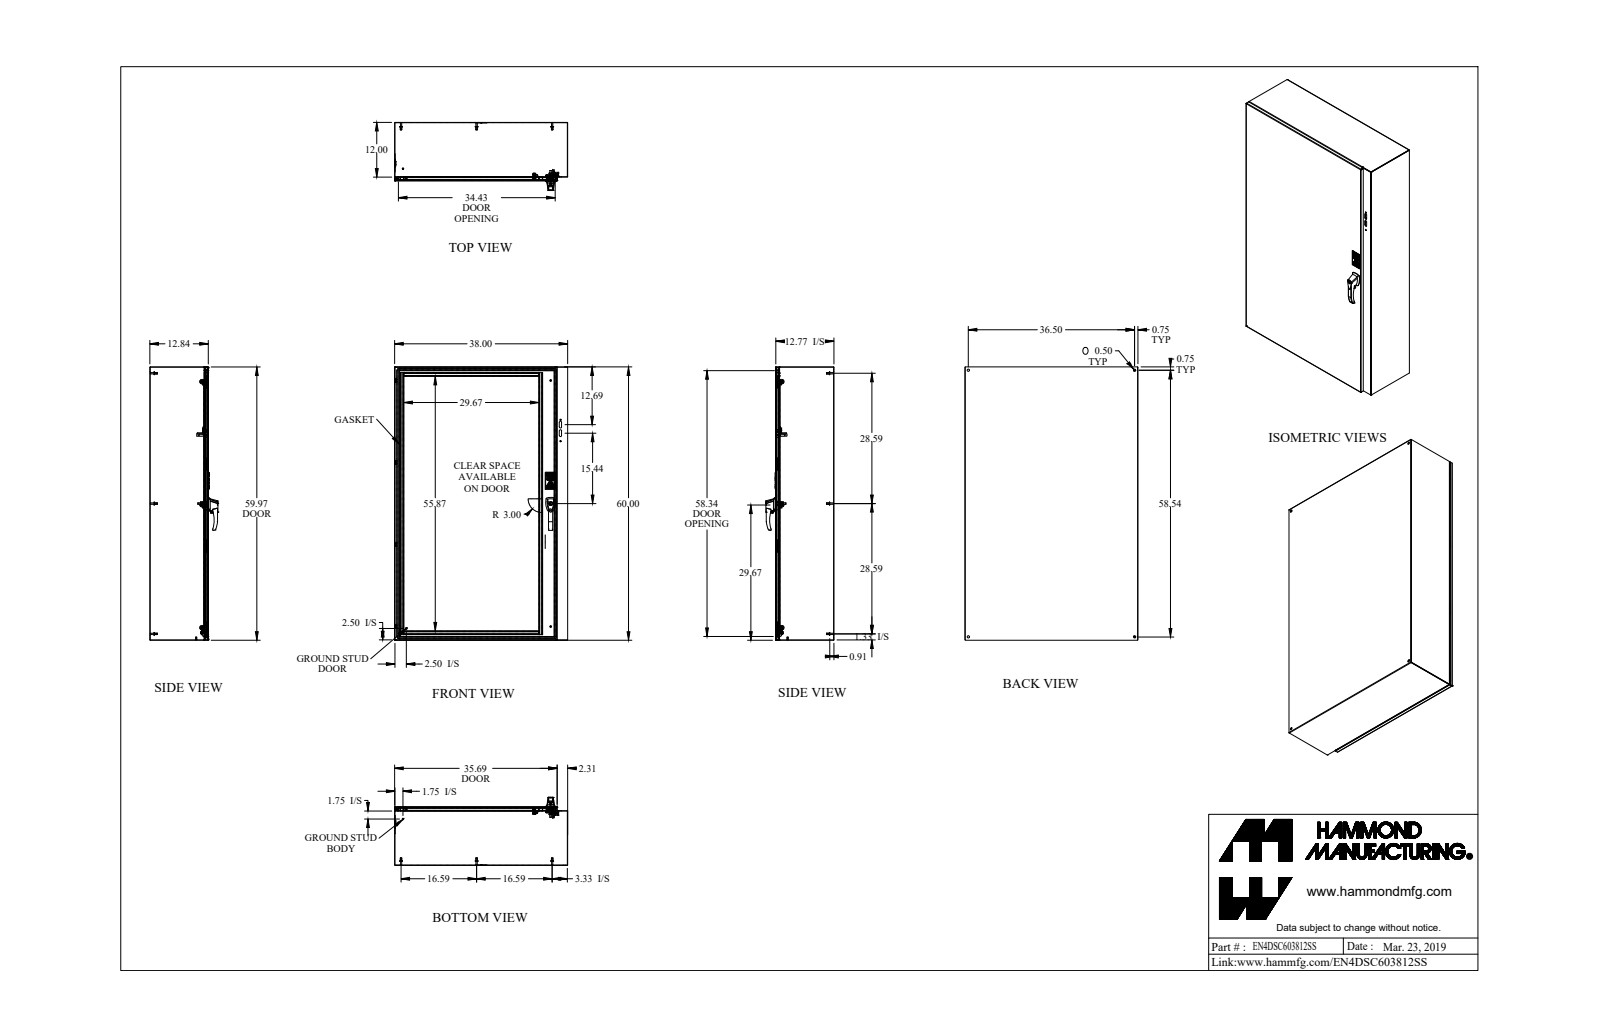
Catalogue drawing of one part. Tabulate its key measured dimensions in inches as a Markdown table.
| quantity | value |
| --- | --- |
| part name | EN4DSC603812SS |
| STEP written by | SolidWorks 2019 (AUTOMOTIVE_DESIGN) |
| units | inches |
| bodies | 75 solids, 1578 faces (889 planar, 476 cylindrical, 213 other) |
| overall size | 60 × 38 × 14.952 |
| volume | 582.6 in³ |
| surface area | 16 197 in² |
| round holes (diameter × count) | 0.176 × 6, 0.5 × 4, 0.196 × 3, 0.25 × 3, 0.265 × 3, 0.413 × 3, 0.156 × 2, 0.173 × 2, 0.215 × 2, 0.256 × 2, 0.281 × 2, 0.313 × 2 |
| round bosses / shafts (diameter × count) | 0.25 × 9, 0.625 × 8, 0.313 × 8, 0.27 × 8, 0.156 × 6, 0.375 × 5, 1 × 3, 0.63 × 2 |
| partial cylindrical surfaces (radius × count) | 0.043 × 24, 0.036 × 18, 0.108 × 18, 0.062 × 17, 0.25 × 15, 0.03 × 14, 0.125 × 14, 0.094 × 10 |
| main face-to-face distances | 0.072, 12.765, 12.693, 12.837, 37.928, 59.928, 37.856, 38, 0.837, 11.928 |
| hole center spacings | 27, 1.11, 2.883, 27, 27.001, 32.722, 36.5, 44.37 |
